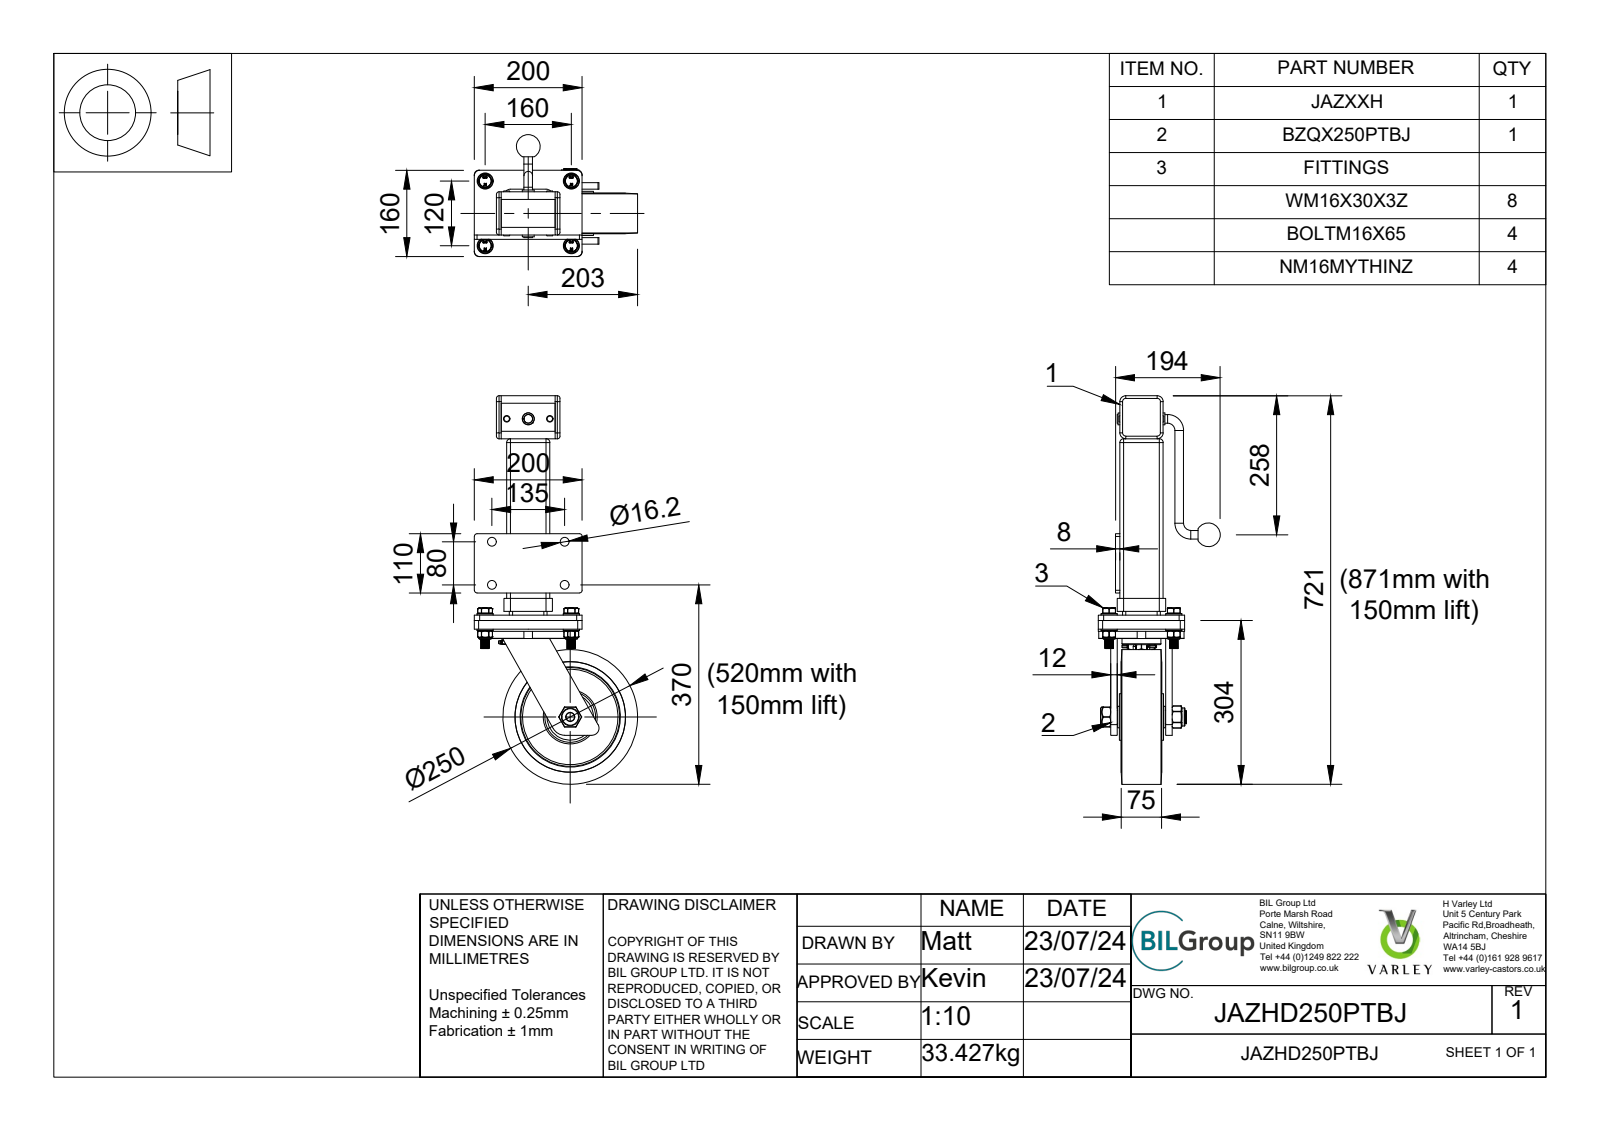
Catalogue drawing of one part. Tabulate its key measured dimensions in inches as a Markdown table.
| quantity | value |
| --- | --- |
| part name | JAZHD250PTBJ v4; BZQX250AS v1; FABRICATED STEEL TOP PLATE; FABRICATED STEEL TOP PLATE Geometry (+8 more) |
| STEP written by | Autodesk Translation Framework v13.14.0.145 (AUTOMOTIVE_DESIGN) |
| units | inches |
| bodies | 73 solids, 2206 faces (635 planar, 800 cylindrical, 771 other) |
| overall size | 28.386 × 11.929 × 8.898 |
| volume | 328.8 in³ |
| surface area | 2 029 in² |
| round holes (diameter × count) | 0.295 × 18, 0.638 × 9, 0.63 × 4, 0.689 × 4, 0.709 × 4, 0.394 × 2, 0.157 × 1, 0.213 × 1, 0.315 × 1, 0.622 × 1, 0.87 × 1, 0.984 × 1 |
| round bosses / shafts (diameter × count) | 1.181 × 5, 0.925 × 4, 0.906 × 4, 0.623 × 4, 0.533 × 4, 0.63 × 3, 9.843 × 1, 6.299 × 1 |
| partial cylindrical surfaces (radius × count) | 0.02 × 46, 0.049 × 22, 0.039 × 20, 0.226 × 18, 0.026 × 16, 0.05 × 16, 0.197 × 12, 0.079 × 11 |
| main face-to-face distances | 0.118, 0.197, 3.031, 2.835, 0.315, 3.15, 0.394, 0.512, 2.953, 3.346 |
| hole center spacings | 2.598, 3.937, 3.15, 1.575, 3.356, 4.724, 4.757, 5.315 |
